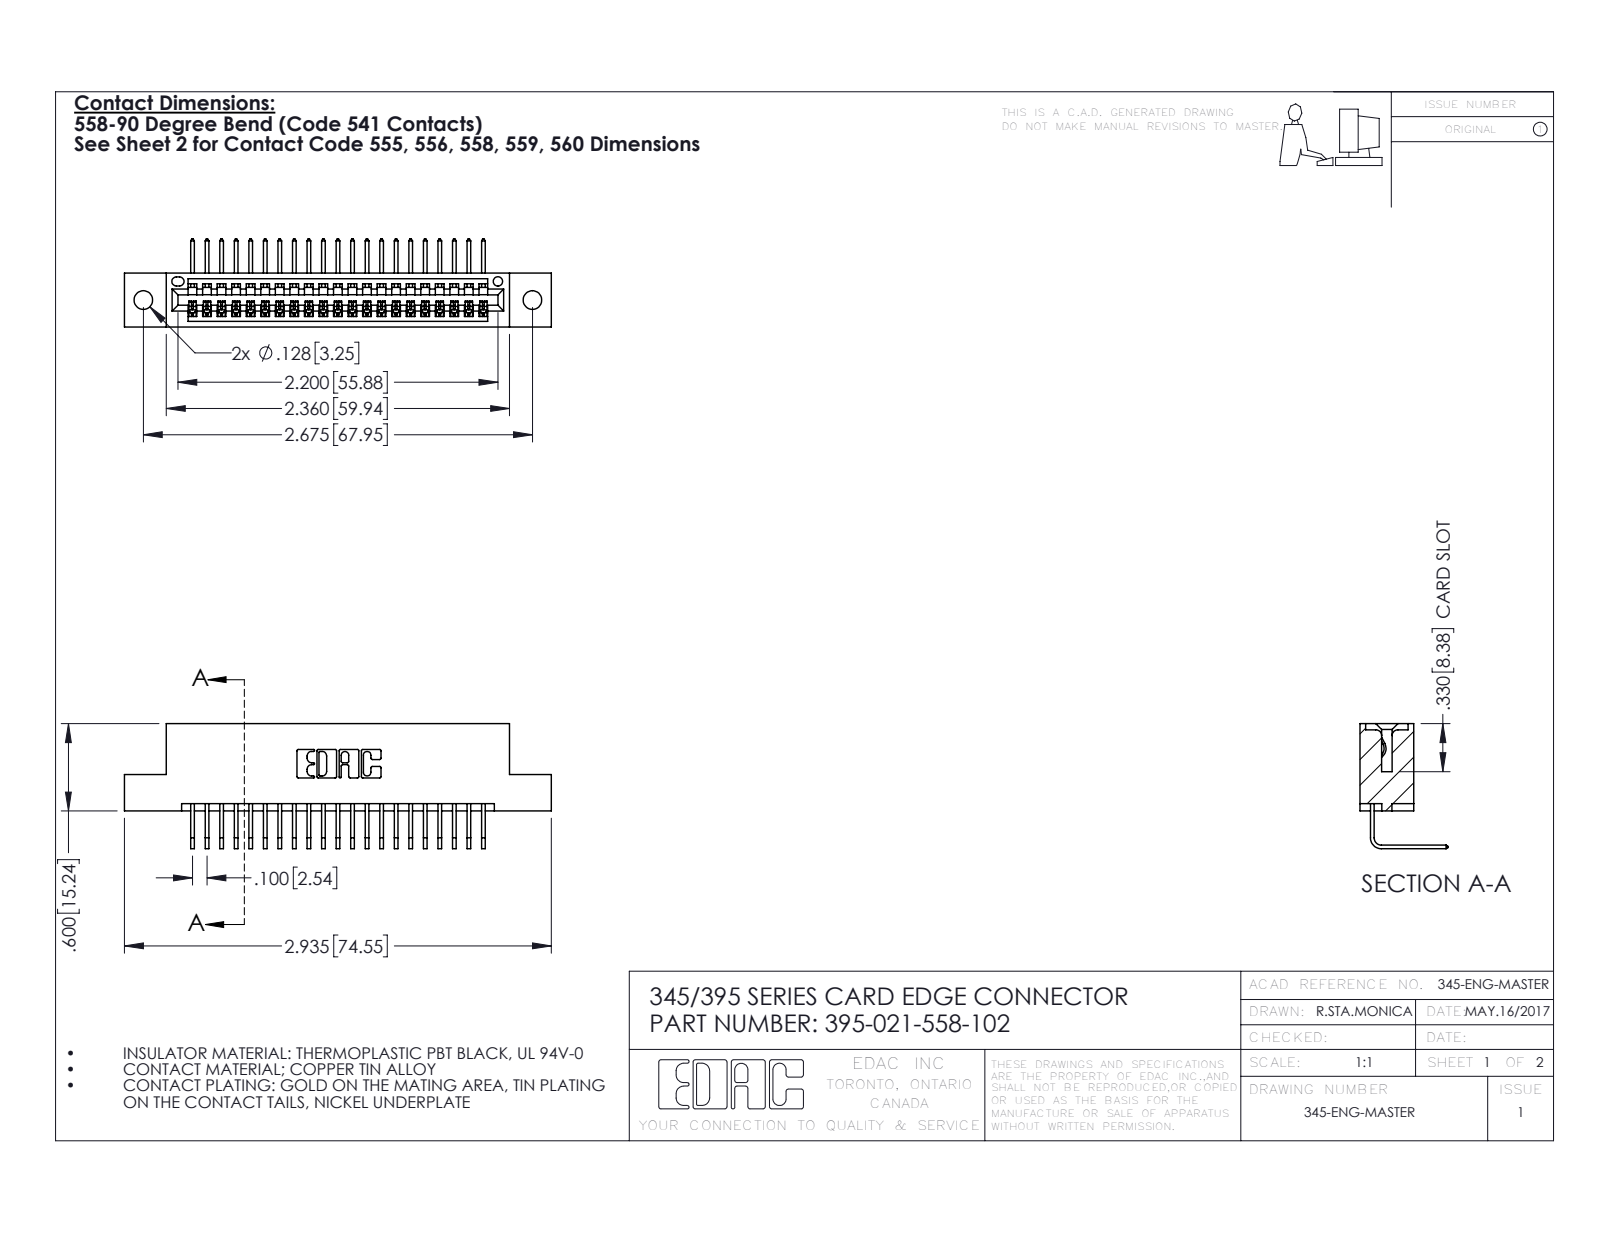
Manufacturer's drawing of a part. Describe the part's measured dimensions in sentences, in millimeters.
The part is named "395-021-558-102; 345-292-001_558 Tail - 2; 345 Part_Flush Mounting Lugs - 0.128 Dia". Its 3-D file was written by "SolidWorks 2016 (CONFIG_CONTROL_DESIGN)". It is 22 solids with 1386 faces: 962 planar, 424 cylindrical and 0 other. Overall it measures 74.5 by 21.8 by 15.4 millimeters. Its volume is 6 950 cubic millimeters and its surface area 9 077 square millimeters. Round holes: 2 of diameter 3.3, 1 of diameter 1.6. Partial cylindrical surfaces (rounded edges, fillets, slot ends): 42 of radius 0.2, 22 of radius 0.3, 6 of radius 0.2, 6 of radius 0.8, 3 of radius 0.7, 2 of radius 0.8, 2 of radius 1, 1 of radius 0.4. The main face-to-face distances are 7.6, 1.8, 5.1, 9.4, 2.5, 6.9, 0.6, 5.7, 3.8, 1.8. The hole center spacings are 6.9, 62, 67.9.
